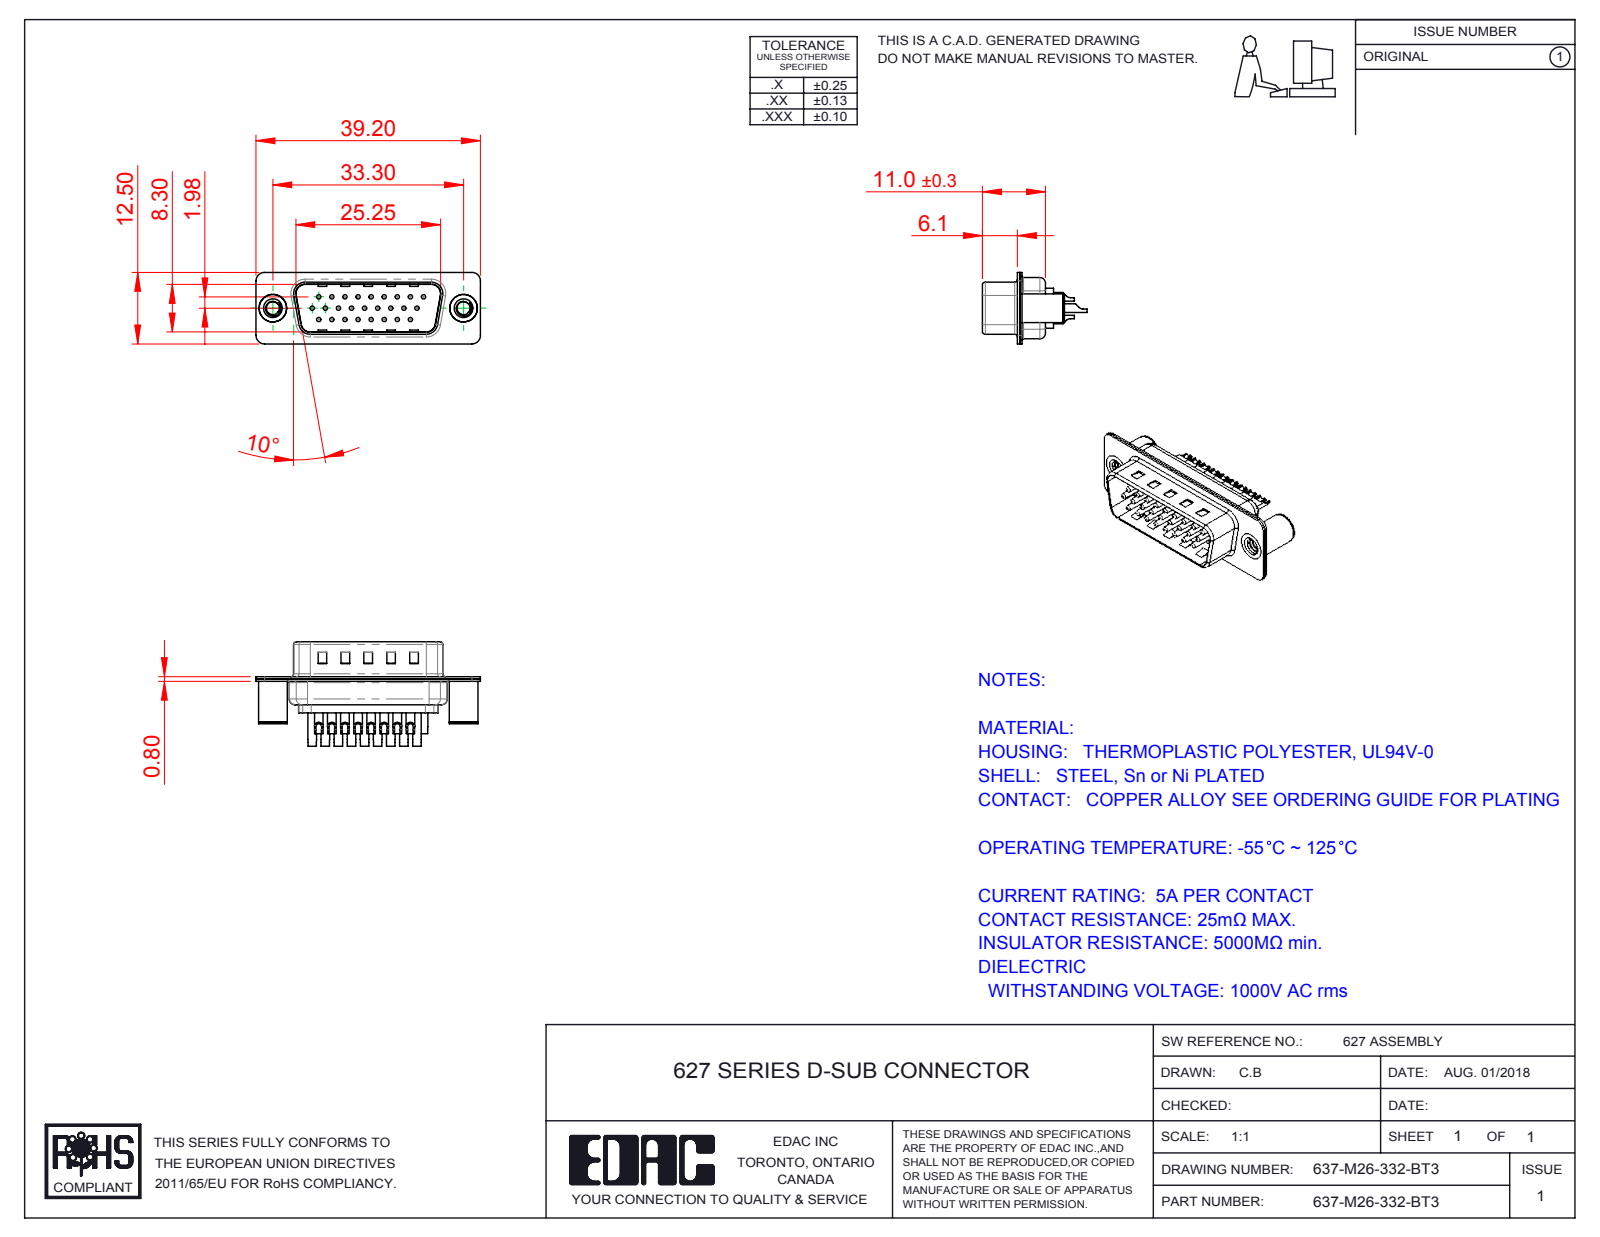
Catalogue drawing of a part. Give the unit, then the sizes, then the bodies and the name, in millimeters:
Units: millimetres
Overall size (bounding box): 39.2 × 18.25 × 12.5
Round holes (diameter × count): ⌀0.75 ×26, ⌀1 ×26, ⌀1.6 ×26, ⌀2 ×26, ⌀2.26 ×2, ⌀3.26 ×2, ⌀4 ×2, ⌀4.8 ×2
Round bosses / shafts (diameter × count): ⌀1.5 ×26, ⌀5 ×2, ⌀4.9 ×2
Partial cylindrical surfaces — rounded edges, fillets, slot ends (radius × count): R1.5 ×16, R2 ×12, R0.5 ×8, R1.6 ×8, R1 ×7, R0.25 ×4, R0.6 ×4, R0.65 ×4
Main face-to-face distances: 0.4, 0.8, 9.5, 9.1, 8.7, 9.9, 0.75, 0.35, 1.2, 1.9
Hole centre spacings: 3.96, 2.28, 4.57, 6.05, 2.29, 8.24, 6.86, 10.48
Volume: 2 118 mm³ · Surface area: 6 331 mm²
Bodies: 31 solids, 1336 faces (373 planar, 573 cylindrical, 390 other)
Part name (STEP PRODUCT): 637M Shell Rear_26 Contacts; 637M 4-40 Threaded Board Spacer; 637-M26-332-BT3; 637M Shell Front_26 Contacts (+4 more)
STEP written by: SolidWorks 2016 (CONFIG_CONTROL_DESIGN)
